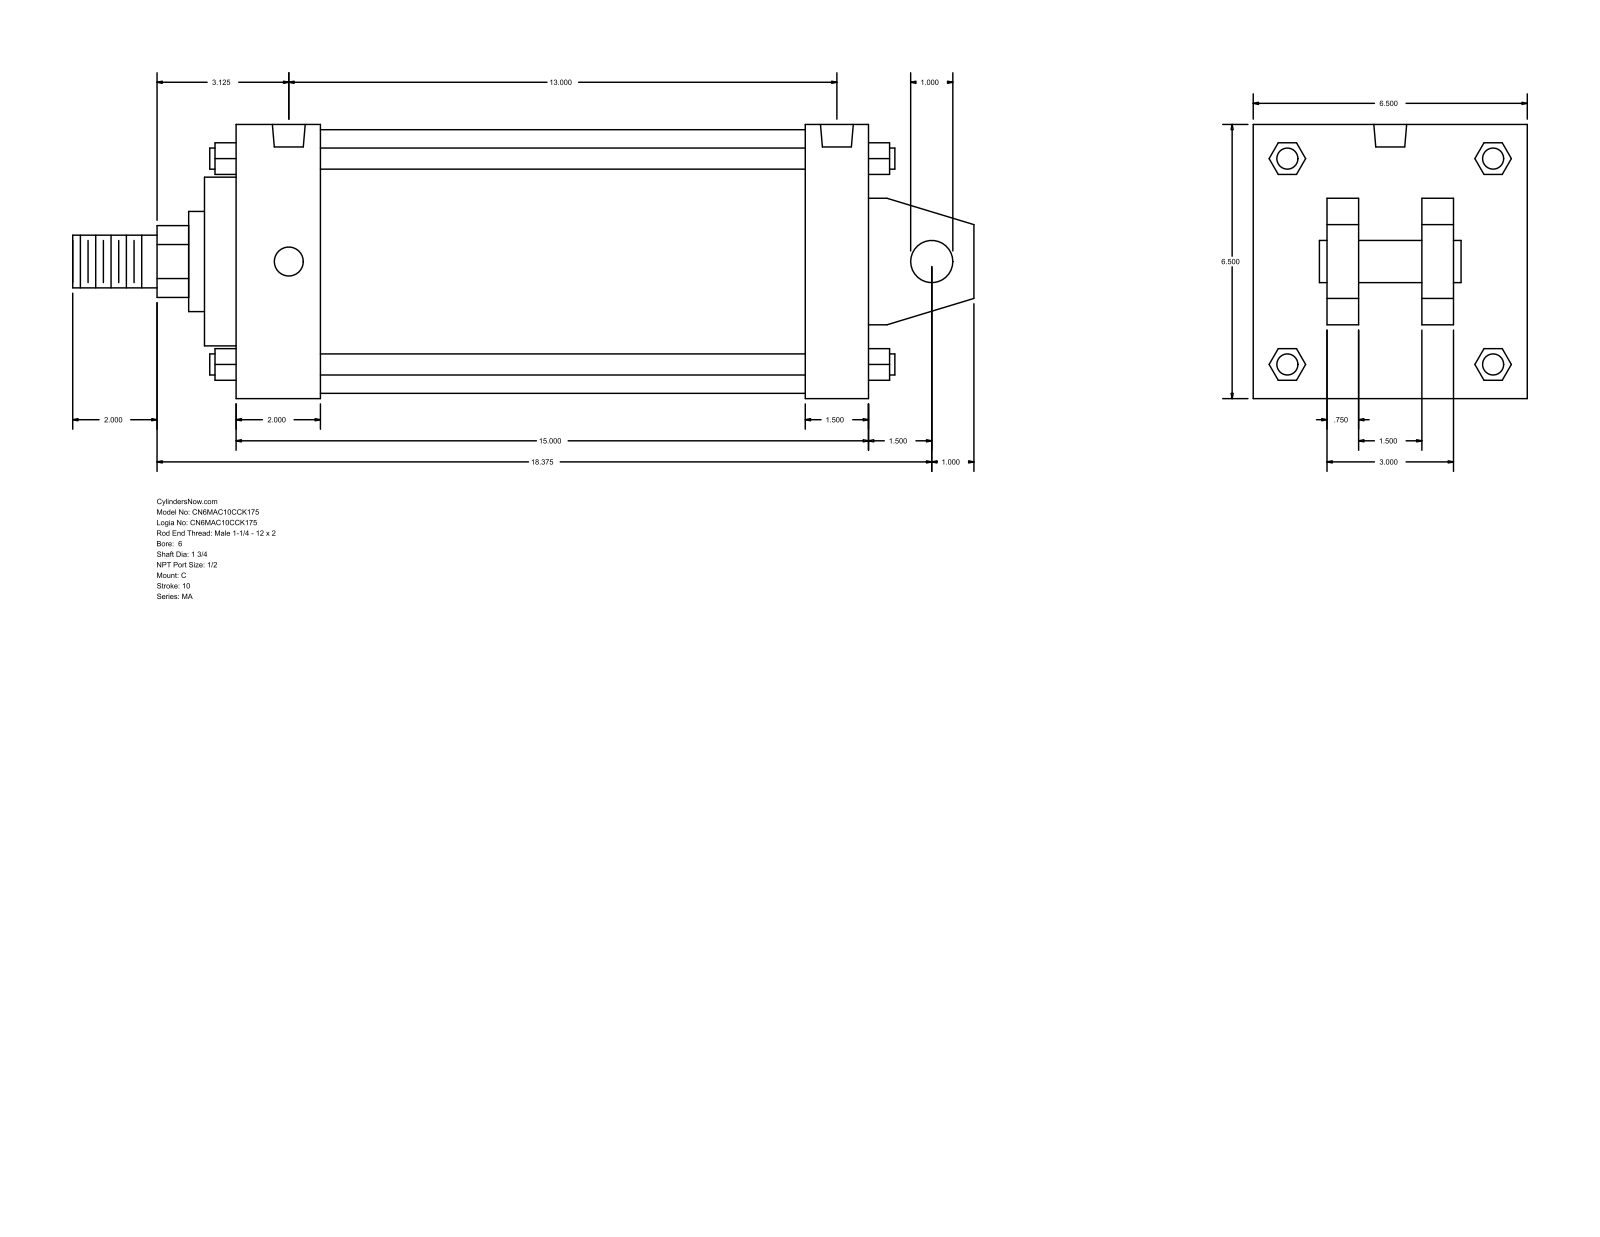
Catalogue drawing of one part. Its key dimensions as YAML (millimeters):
part_name: "MA_C__0600_1.75"
step_written_by: "GSSL Pune (CONFIG_CONTROL_DESIGN)"
units: millimeters
bodies: {solids: 0, faces: 141, planar: 109, cylindrical: 32, other: 0}
overall_size: [542.92, 165.1, 165.1]
round_holes:
  - {diameter: 17.46, count: 4}
  - {diameter: 19.77, count: 2}
round_bosses_or_shafts:
  - {diameter: 12.7, count: 4}
  - {diameter: 158.75, count: 1}
  - {diameter: 101.6, count: 1}
  - {diameter: 60.33, count: 1}
  - {diameter: 44.45, count: 1}
  - {diameter: 31.75, count: 1}
  - {diameter: 25.4, count: 1}
partial_cylinders:
  - {radius: 21.63, count: 1}
face_to_face_distances: [165.1, 381, 19.05, 38.1, 63.5, 101.6, 50.8, 120.65, 44.45, 342.9]
hole_center_spacings: [330.19]
